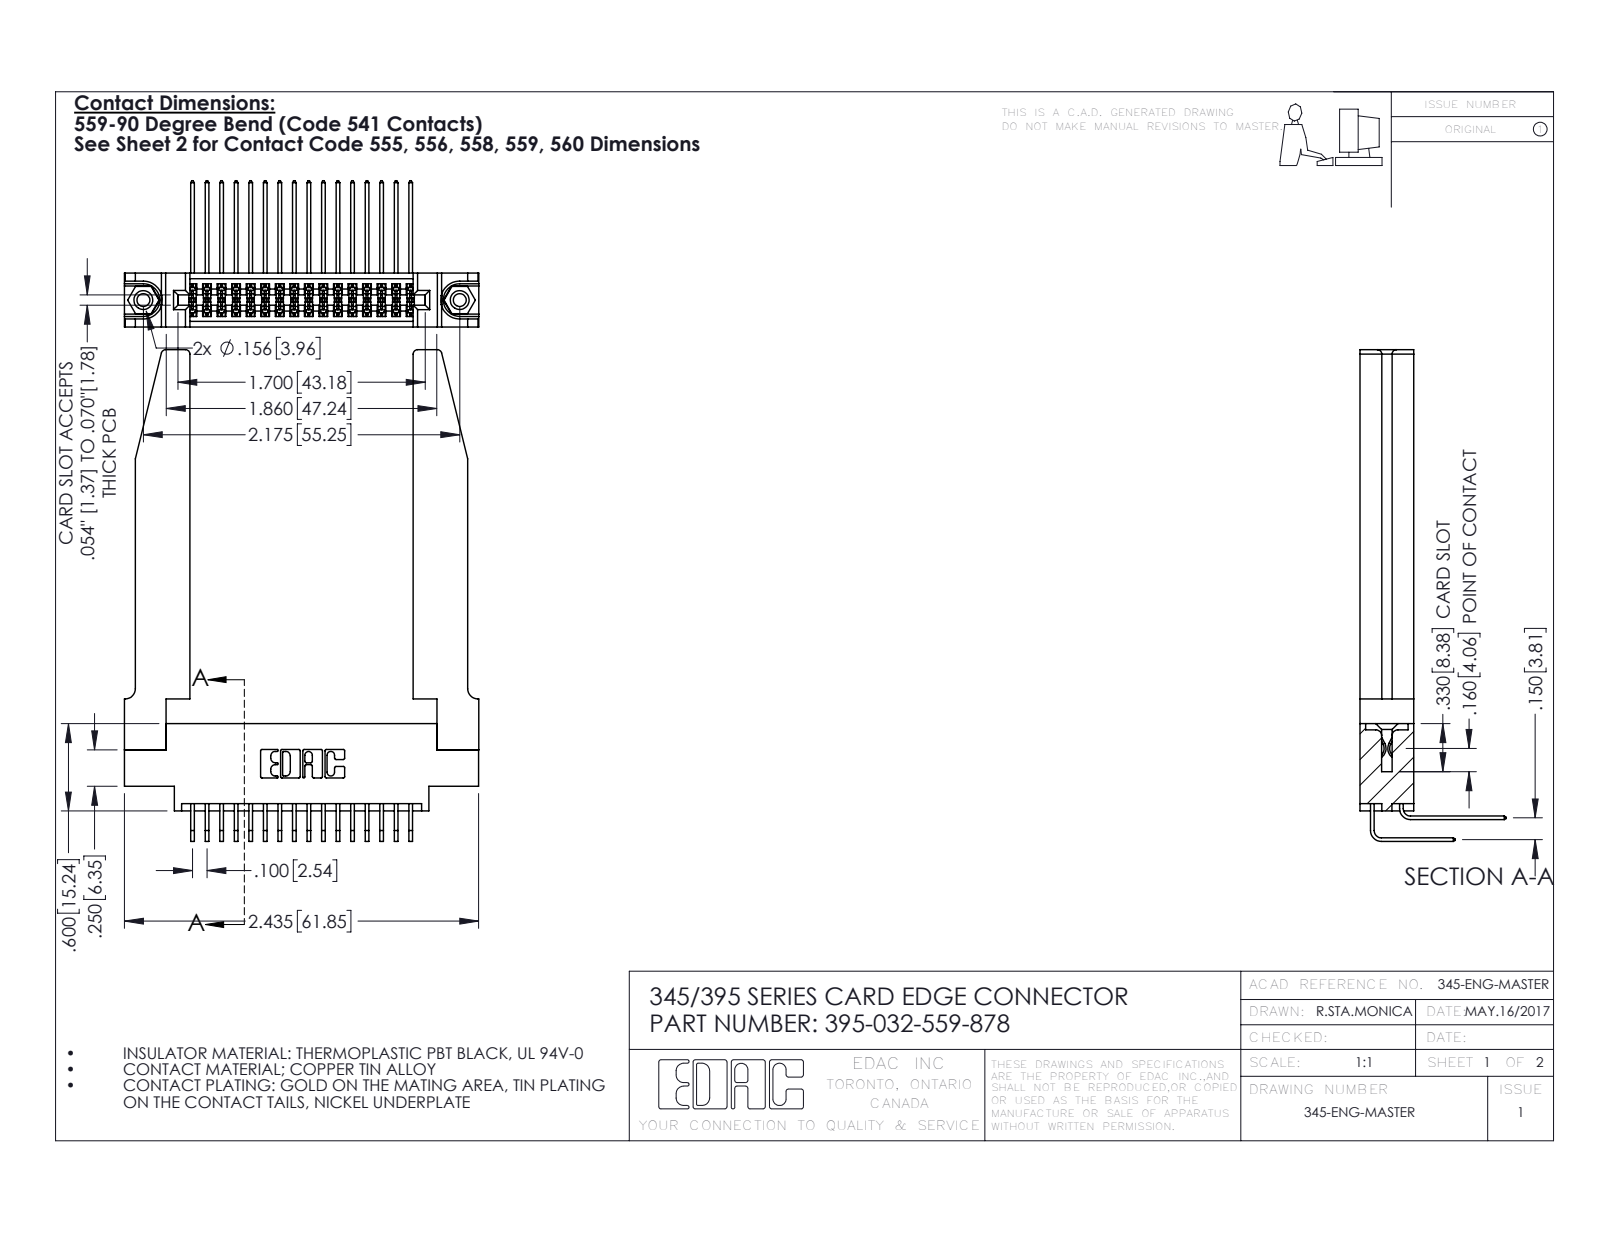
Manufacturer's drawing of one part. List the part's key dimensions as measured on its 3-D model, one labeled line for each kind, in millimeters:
Part name (STEP PRODUCT): 345-292-001_559 Tail - 2; 345-250-001_345-250-001-102; 395-032-559-878; 345-292-001_558 559 Tail - 1 (+2 more)
STEP written by: SolidWorks 2016 (CONFIG_CONTROL_DESIGN)
Units: millimetres
Bodies: 37 solids, 2028 faces (1346 planar, 630 cylindrical, 52 other)
Overall size (bounding box): 85.8 × 61.9 × 25.5
Volume: 13 600 mm³ · Surface area: 15 980 mm²
Round holes (diameter × count): ⌀2.3 ×2, ⌀3.2 ×2, ⌀4 ×2, ⌀1.6 ×1
Round bosses / shafts (diameter × count): ⌀3.9 ×2
Partial cylindrical surfaces — rounded edges, fillets, slot ends (radius × count): R0.2 ×48, R0.3 ×22, R0.8 ×8, R0.2 ×6, R0.8 ×6, R0.7 ×3, R0.4 ×2, R0.5 ×2
Main face-to-face distances: 9.4, 1.8, 7.6, 3.8, 3.8, 2.5, 6.9, 0.6, 5.1, 3.8
Hole centre spacings: 6.9, 49.3, 55.2
